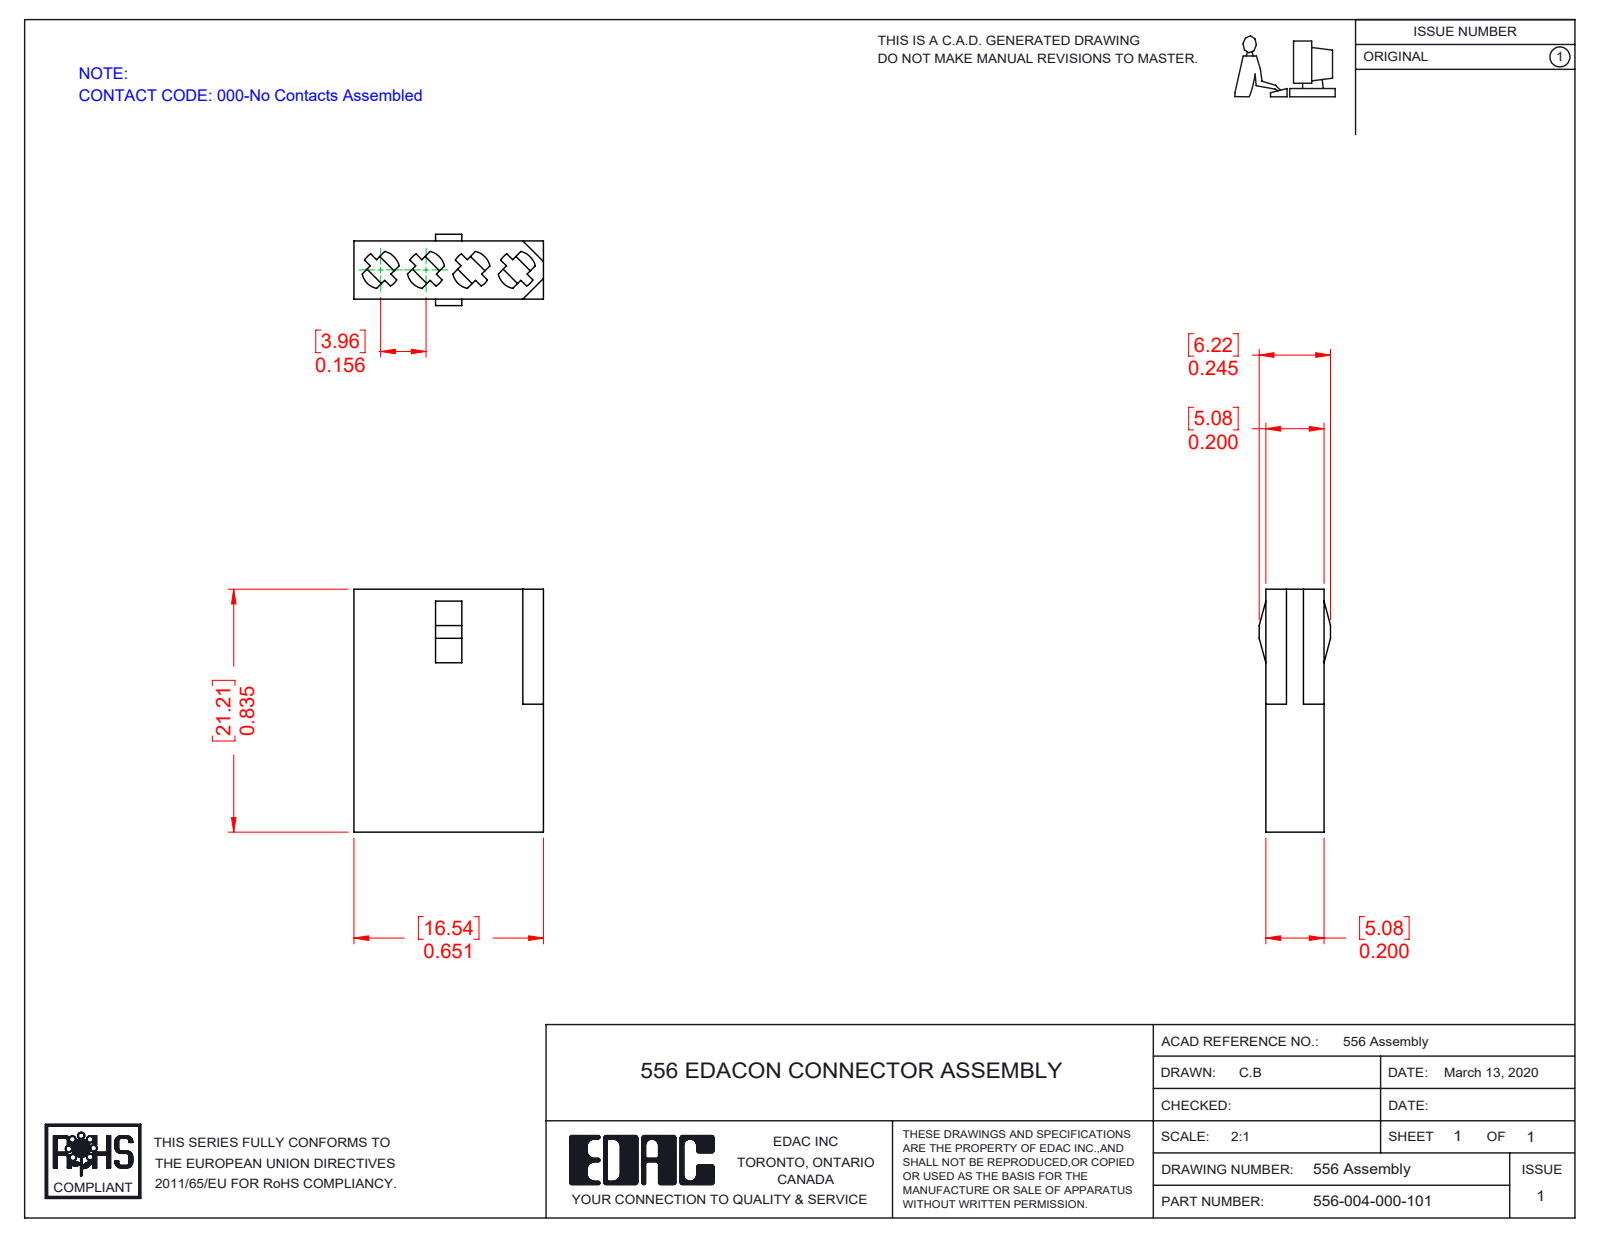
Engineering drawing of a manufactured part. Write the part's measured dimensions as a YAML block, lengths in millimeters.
part_name: "556-210-001_556-004-000-101; 556-004-000-101"
step_written_by: "SolidWorks 2016 (CONFIG_CONTROL_DESIGN)"
units: millimeters
bodies: {solids: 1, faces: 124, planar: 92, cylindrical: 24, other: 8}
overall_size: [21.21, 16.54, 6.22]
volume: 1145
surface_area: 1999
round_holes:
  - {diameter: 3.35, count: 4}
partial_cylinders:
  - {radius: 1.65, count: 4}
face_to_face_distances: [5.08, 2.8, 5.6, 1.78, 4.58, 16.53, 0.76, 2.04, 7.38, 1.02]
hole_center_spacings: [3.96, 3.97, 7.92, 7.93, 11.89]
